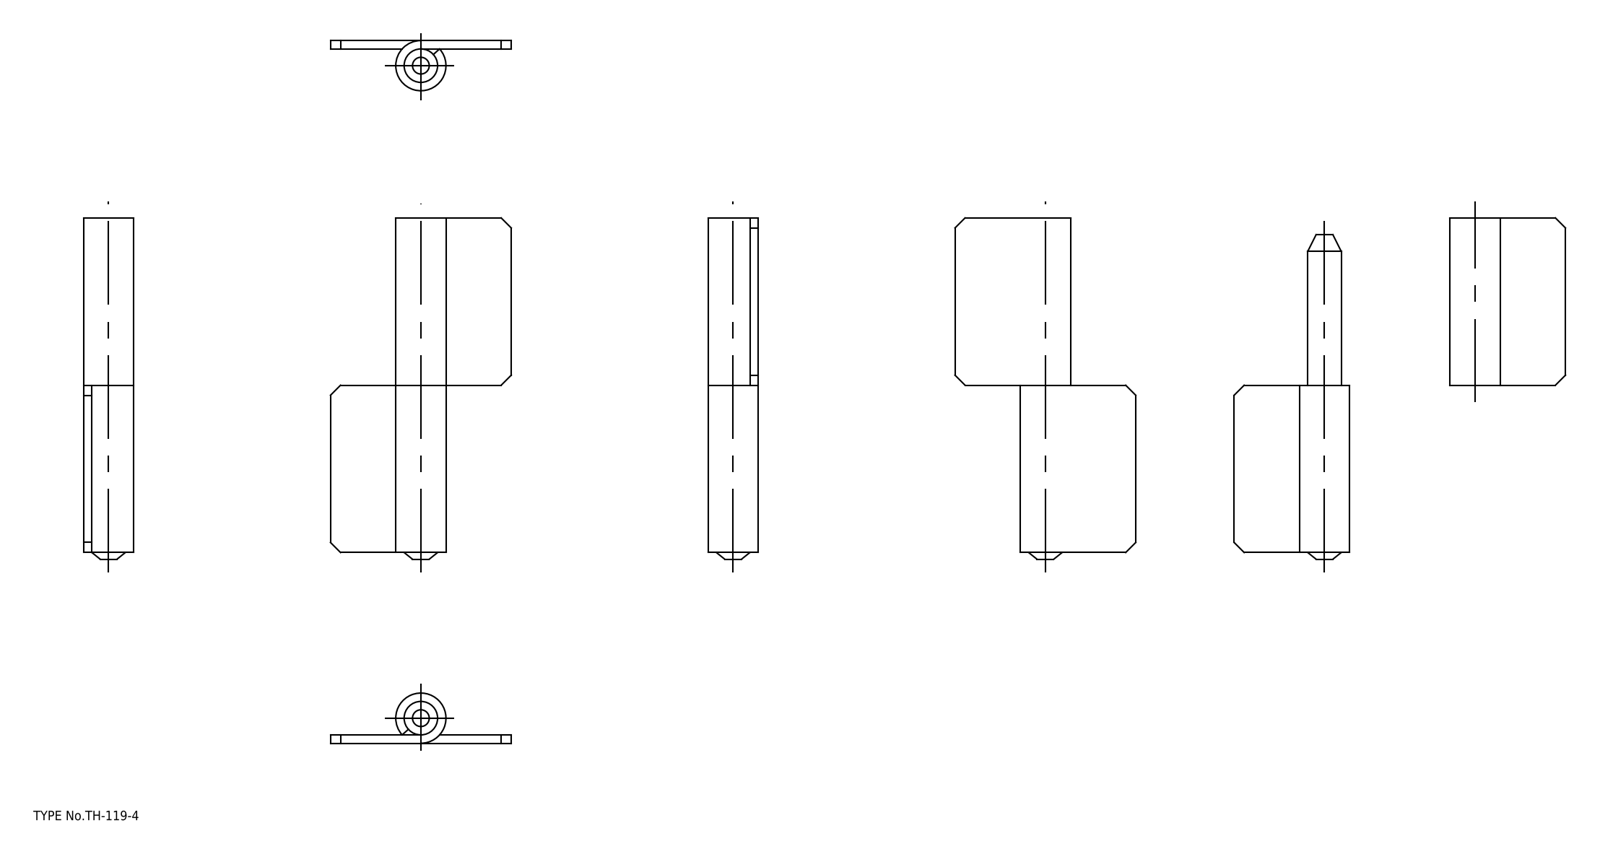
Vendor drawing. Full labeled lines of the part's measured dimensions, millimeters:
Part name (STEP PRODUCT): ヒンジピース(A)組立; ヒンジピース(B)
STEP written by: spGate 16.7.1 (AUTOMOTIVE_DESIGN)
Units: millimetres
Bodies: 2 solids, 27 faces (18 planar, 5 cylindrical, 4 other)
Overall size (bounding box): 102 × 54 × 15
Volume: 22 604 mm³ · Surface area: 13 612 mm²
Round bosses / shafts (diameter × count): ⌀15 ×1, ⌀10 ×1
Main face-to-face distances: 2.5, 50, 100, 54, 5, 102, 45, 95, 97, 52
